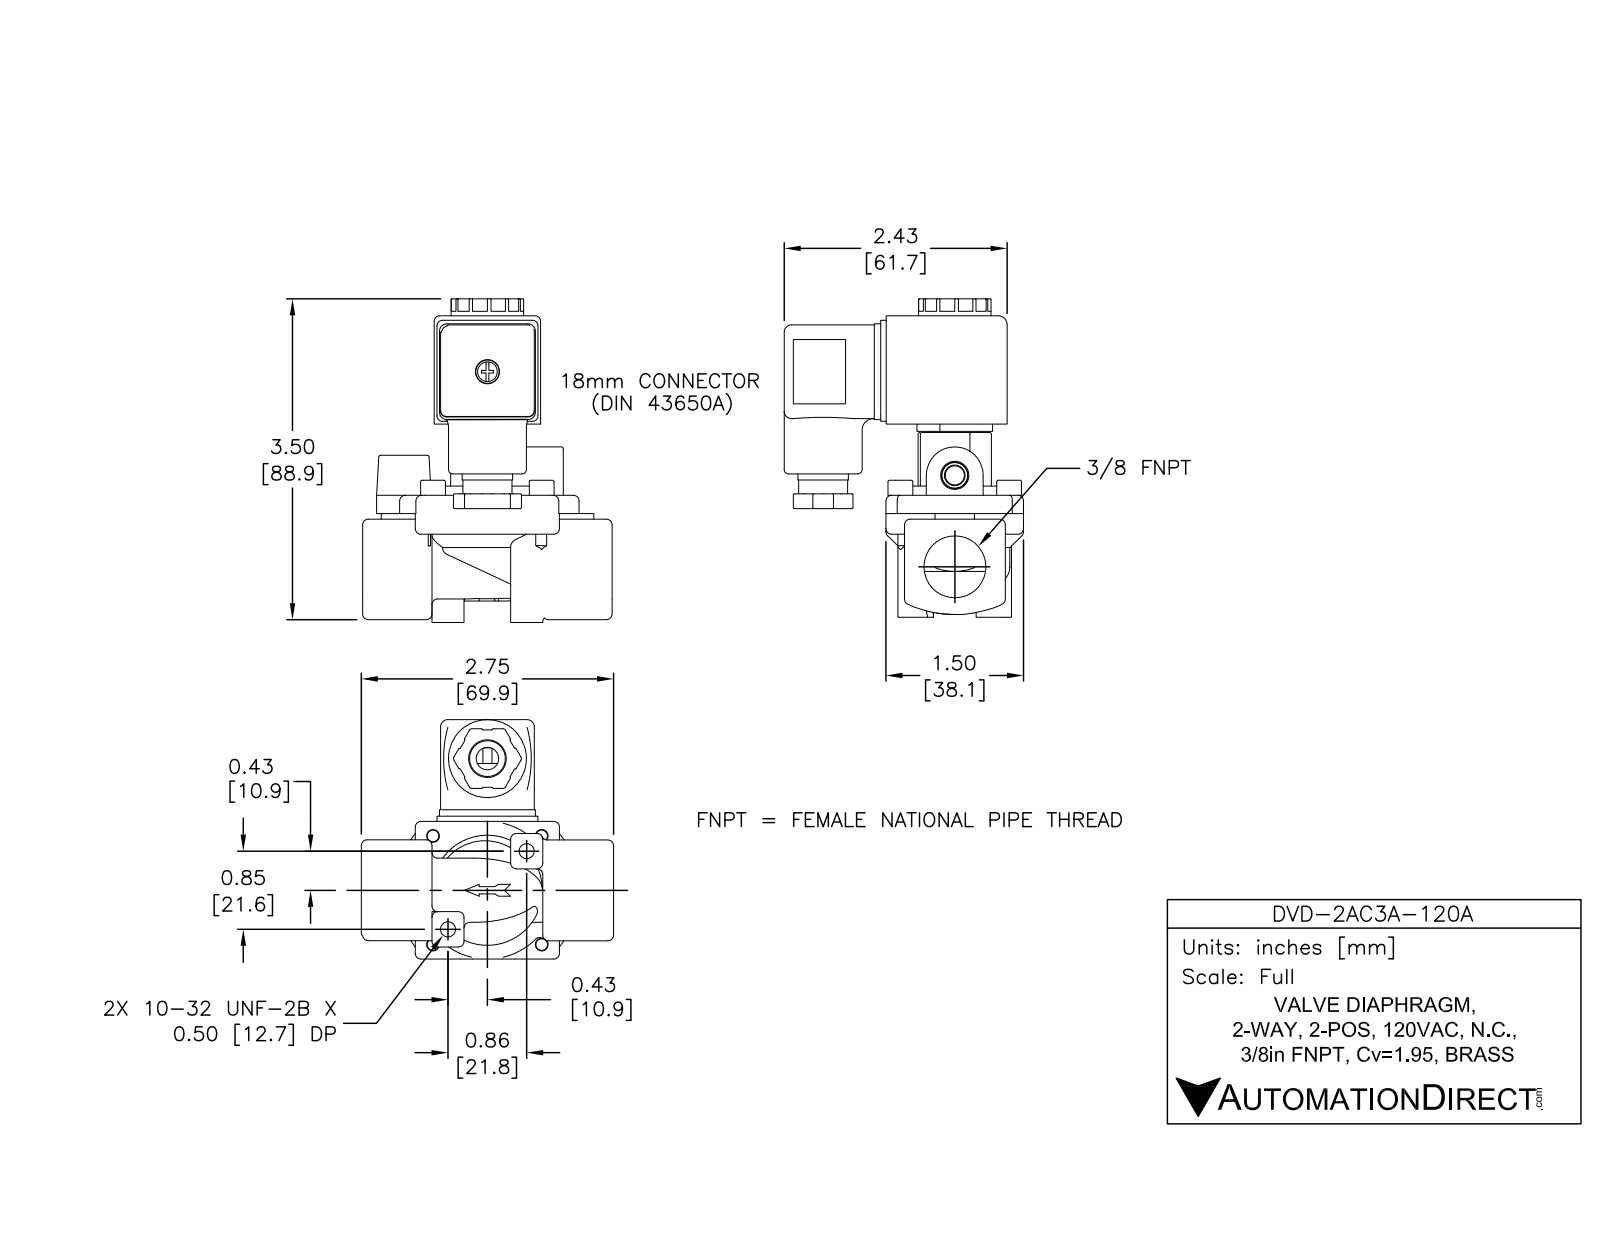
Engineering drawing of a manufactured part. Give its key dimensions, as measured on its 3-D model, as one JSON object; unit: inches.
{"part_name": "DVD-2AC3A-120A", "step_written_by": "SolidWorks 2015 (AUTOMOTIVE_DESIGN)", "units": "inches", "bodies": {"solids": 8, "faces": 1959, "planar": 871, "cylindrical": 435, "other": 653}, "overall_size": [3.439, 2.722, 2.62], "volume_in3": 5.764, "surface_area_in2": 71.06, "round_holes": [[0.13, 4], [0.164, 4], [0.156, 3], [0.038, 2], [0.06, 2], [0.098, 2], [0.14, 2], [0.5, 2], [0.062, 1], [0.077, 1], [0.089, 1], [0.093, 1]], "round_bosses_or_shafts": [[0.27, 4], [0.177, 4], [0.16, 4], [1.375, 1], [1.37, 1], [0.85, 1], [0.79, 1], [0.609, 1]], "partial_cylinders_radius": [[0.01, 52], [0.062, 46], [0.031, 17], [0.08, 12], [0.156, 12], [0.05, 8], [0.03, 6], [0.062, 5]], "face_to_face_distances": [1.161, 0.925, 0.2, 0.078, 1.1, 1.043, 0.965, 0.257, 1.3, 0.021], "hole_center_spacings": [0.924, 0.311, 0.617, 0.838, 1.172, 1.185, 0.747, 0.924]}
